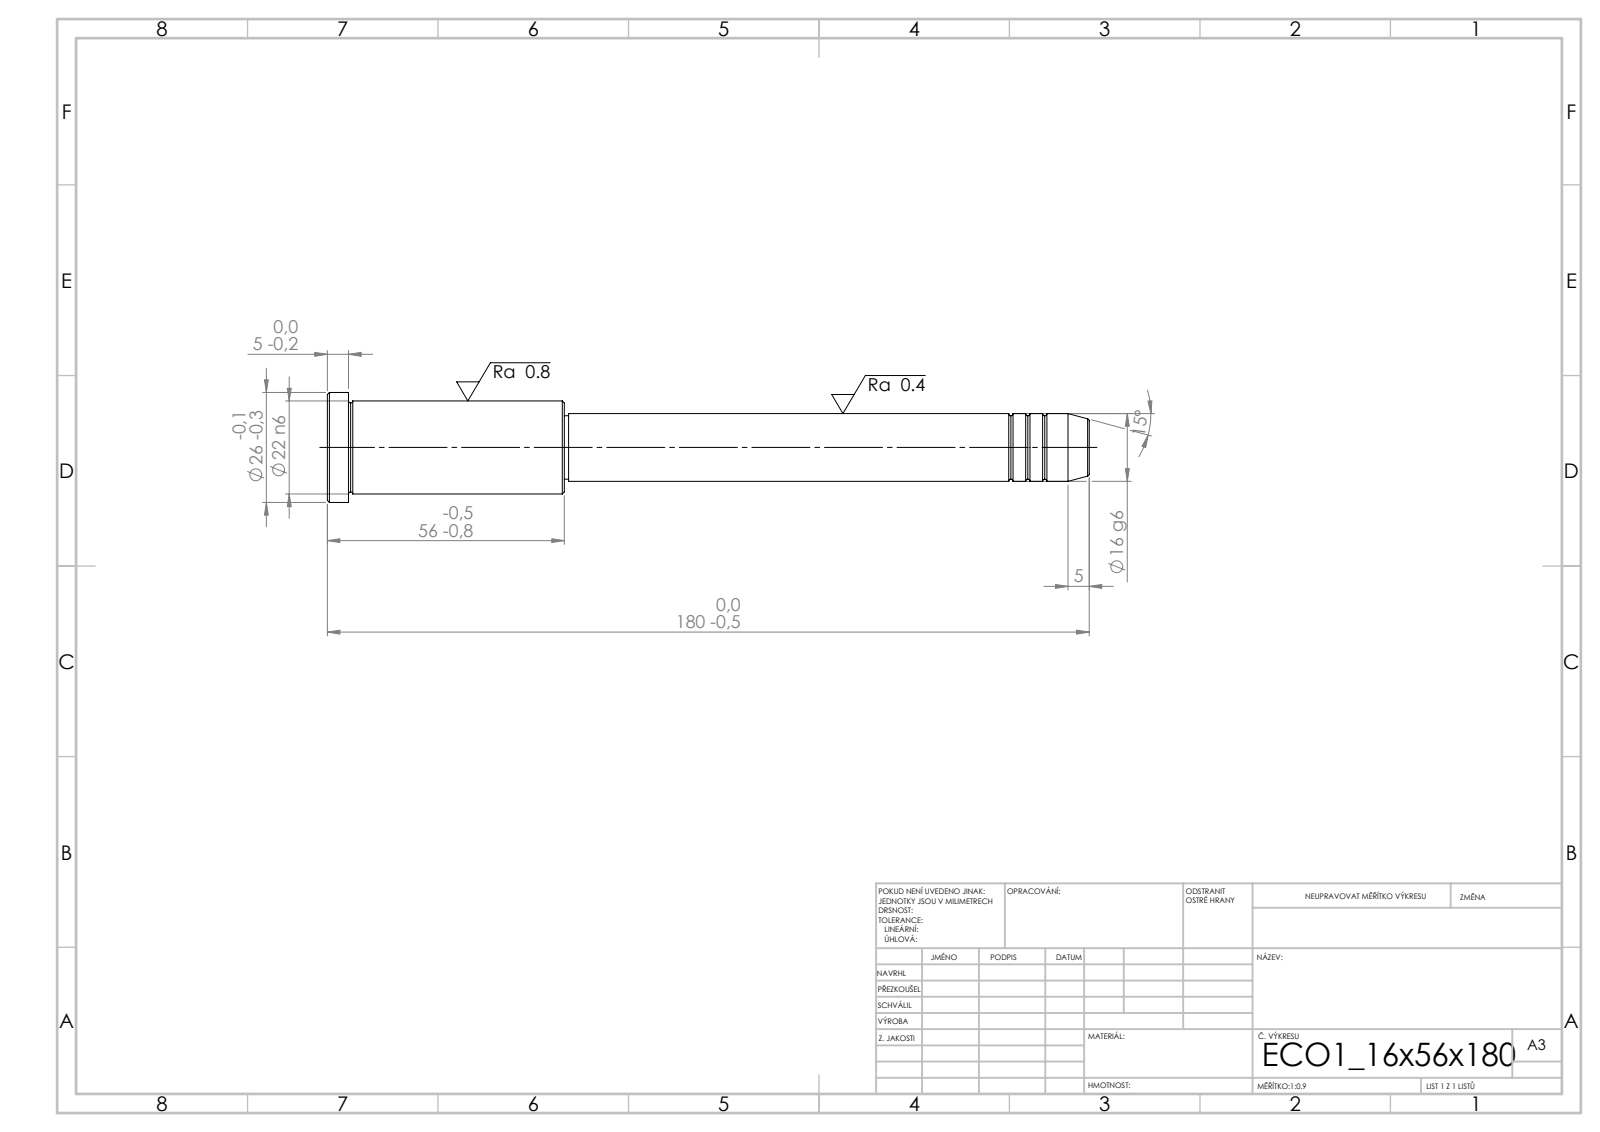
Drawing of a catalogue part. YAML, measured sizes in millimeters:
step_written_by: "SolidWorks 2019 (CONFIG_CONTROL_DESIGN)"
units: millimeters
bodies: {solids: 1, faces: 43, planar: 5, cylindrical: 14, other: 24}
overall_size: [180, 26, 26]
volume: 46686
surface_area: 11262
round_bosses_or_shafts:
  - {diameter: 26, count: 1}
  - {diameter: 22, count: 1}
  - {diameter: 16, count: 1}
  - {diameter: 15, count: 1}
face_to_face_distances: [56, 51, 5, 124, 175, 180, 123, 1, 52, 57]
